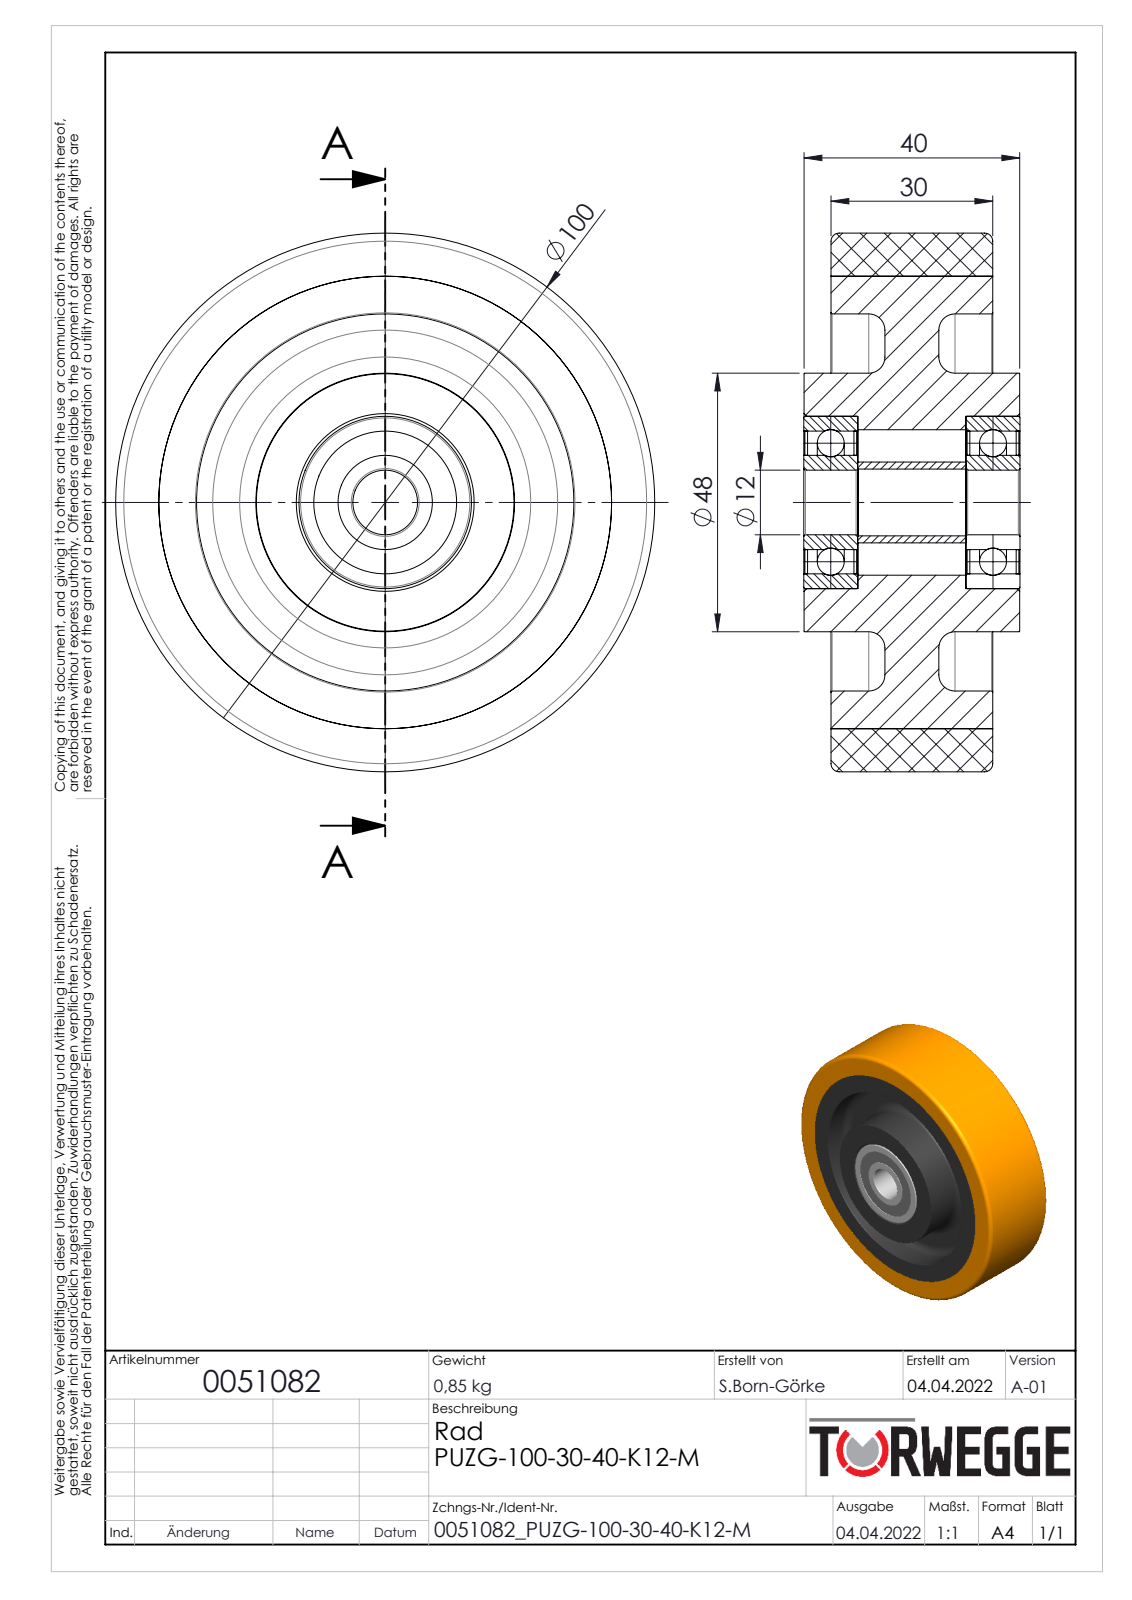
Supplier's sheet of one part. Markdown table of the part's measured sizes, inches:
| quantity | value |
| --- | --- |
| part name | 0051082 |
| STEP written by | SolidWorks 2020 (AUTOMOTIVE_DESIGN) |
| units | inches |
| bodies | 13 solids, 160 faces (28 planar, 64 cylindrical, 68 other) |
| overall size | 3.937 × 3.937 × 1.579 |
| volume | 12.11 in³ |
| surface area | 100.4 in² |
| round holes (diameter × count) | 0.472 × 1, 0.488 × 1, 0.689 × 1, 1.043 × 1, 1.063 × 1, 1.26 × 1, 2.756 × 1, 3.307 × 1 |
| round bosses / shafts (diameter × count) | 3.937 × 1, 1.89 × 1, 0.591 × 1 |
| main face-to-face distances | 1.181, 0.394, 0.197, 0.984, 0.591, 0.787, 1.185, 1.378, 0.199, 0.593 |
